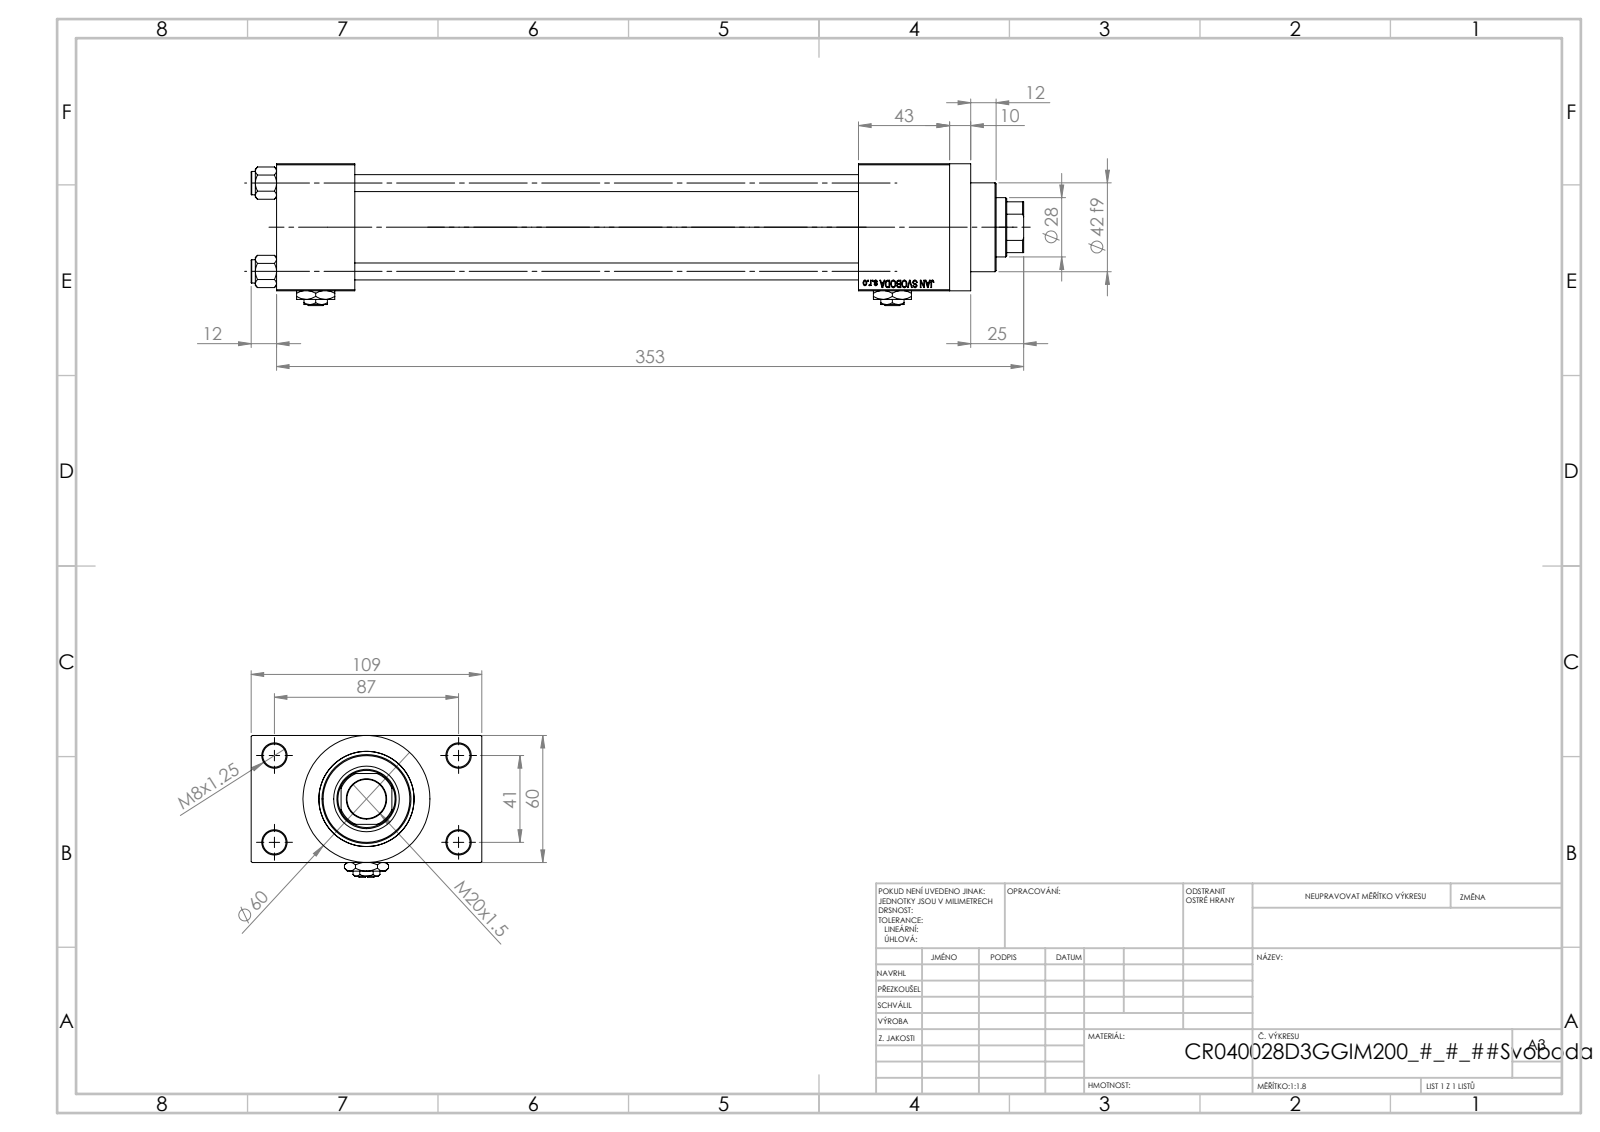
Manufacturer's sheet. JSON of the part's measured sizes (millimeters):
{"part_name": "V215CR_VCP_D; Zatka_pro_OIL_PORT; V215CR_D_Body; V215CR_D_TYCINKA (+2 more)", "step_written_by": "SolidWorks 2019 (CONFIG_CONTROL_DESIGN)", "units": "millimeters", "bodies": {"solids": 13, "faces": 1206, "planar": 546, "cylindrical": 100, "other": 560}, "overall_size": [365, 109, 67], "volume_mm3": 751920, "surface_area_mm2": 213036, "round_holes": [[8, 4], [11, 4], [7, 2], [16.66, 2], [24, 2], [18.5, 1], [28, 1], [31, 1], [40, 1], [45, 1]], "round_bosses_or_shafts": [[11, 4], [60, 1], [46, 1], [42, 1]], "partial_cylinders_radius": [[13.5, 1]], "face_to_face_distances": [60, 24.5, 84.5, 238, 37, 275, 318, 281, 43, 109], "hole_center_spacings": [22.65, 29.49, 41.7, 47.15, 48.09, 64.35, 76.49, 41]}
